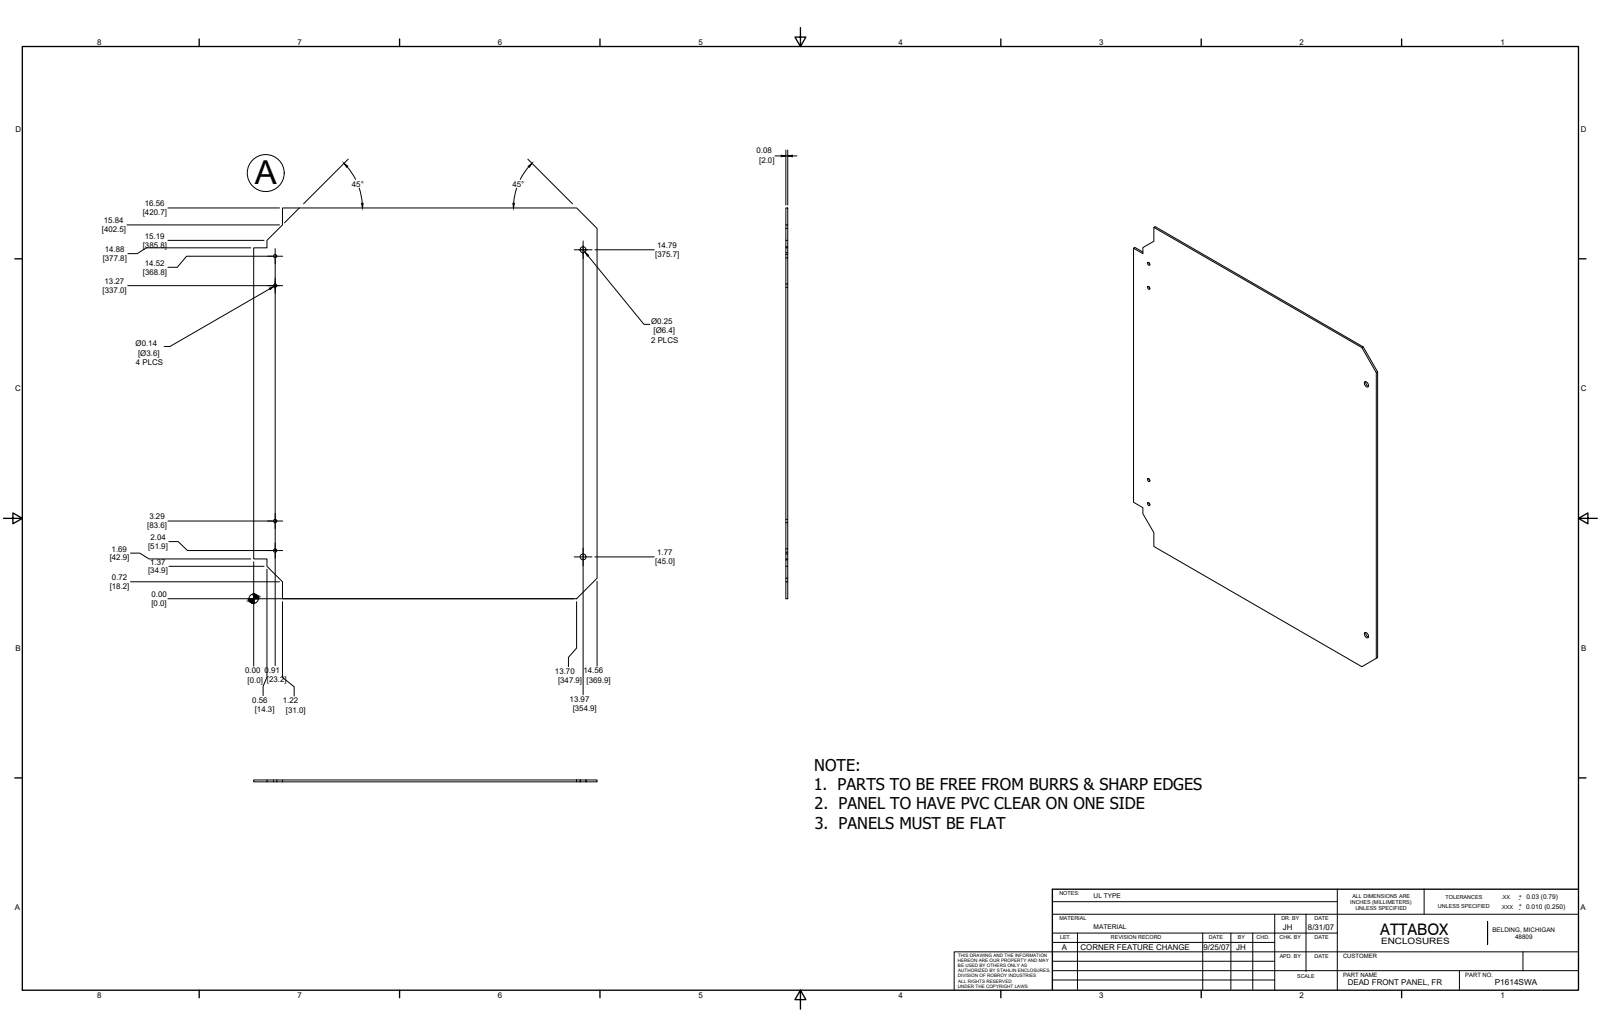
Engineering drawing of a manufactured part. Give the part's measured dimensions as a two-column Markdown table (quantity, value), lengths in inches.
| quantity | value |
| --- | --- |
| part name | P1614SWAL |
| STEP written by | Autodesk Inventor 11 (AUTOMOTIVE_DESIGN) |
| units | inches |
| bodies | 1 solid, 20 faces (14 planar, 6 cylindrical, 0 other) |
| overall size | 16.563 × 14.563 × 0.08 |
| volume | 19.05 in³ |
| surface area | 481.3 in² |
| round holes (diameter × count) | 0.14 × 4, 0.25 × 2 |
| main face-to-face distances | 0.08, 14.562, 16.562, 1.09, 15.472, 13.472, 20.155, 14.383 |
| hole center spacings | 1.25, 11.226, 13.063, 13.148, 17.4, 18.25, 9.976, 12.476 |
